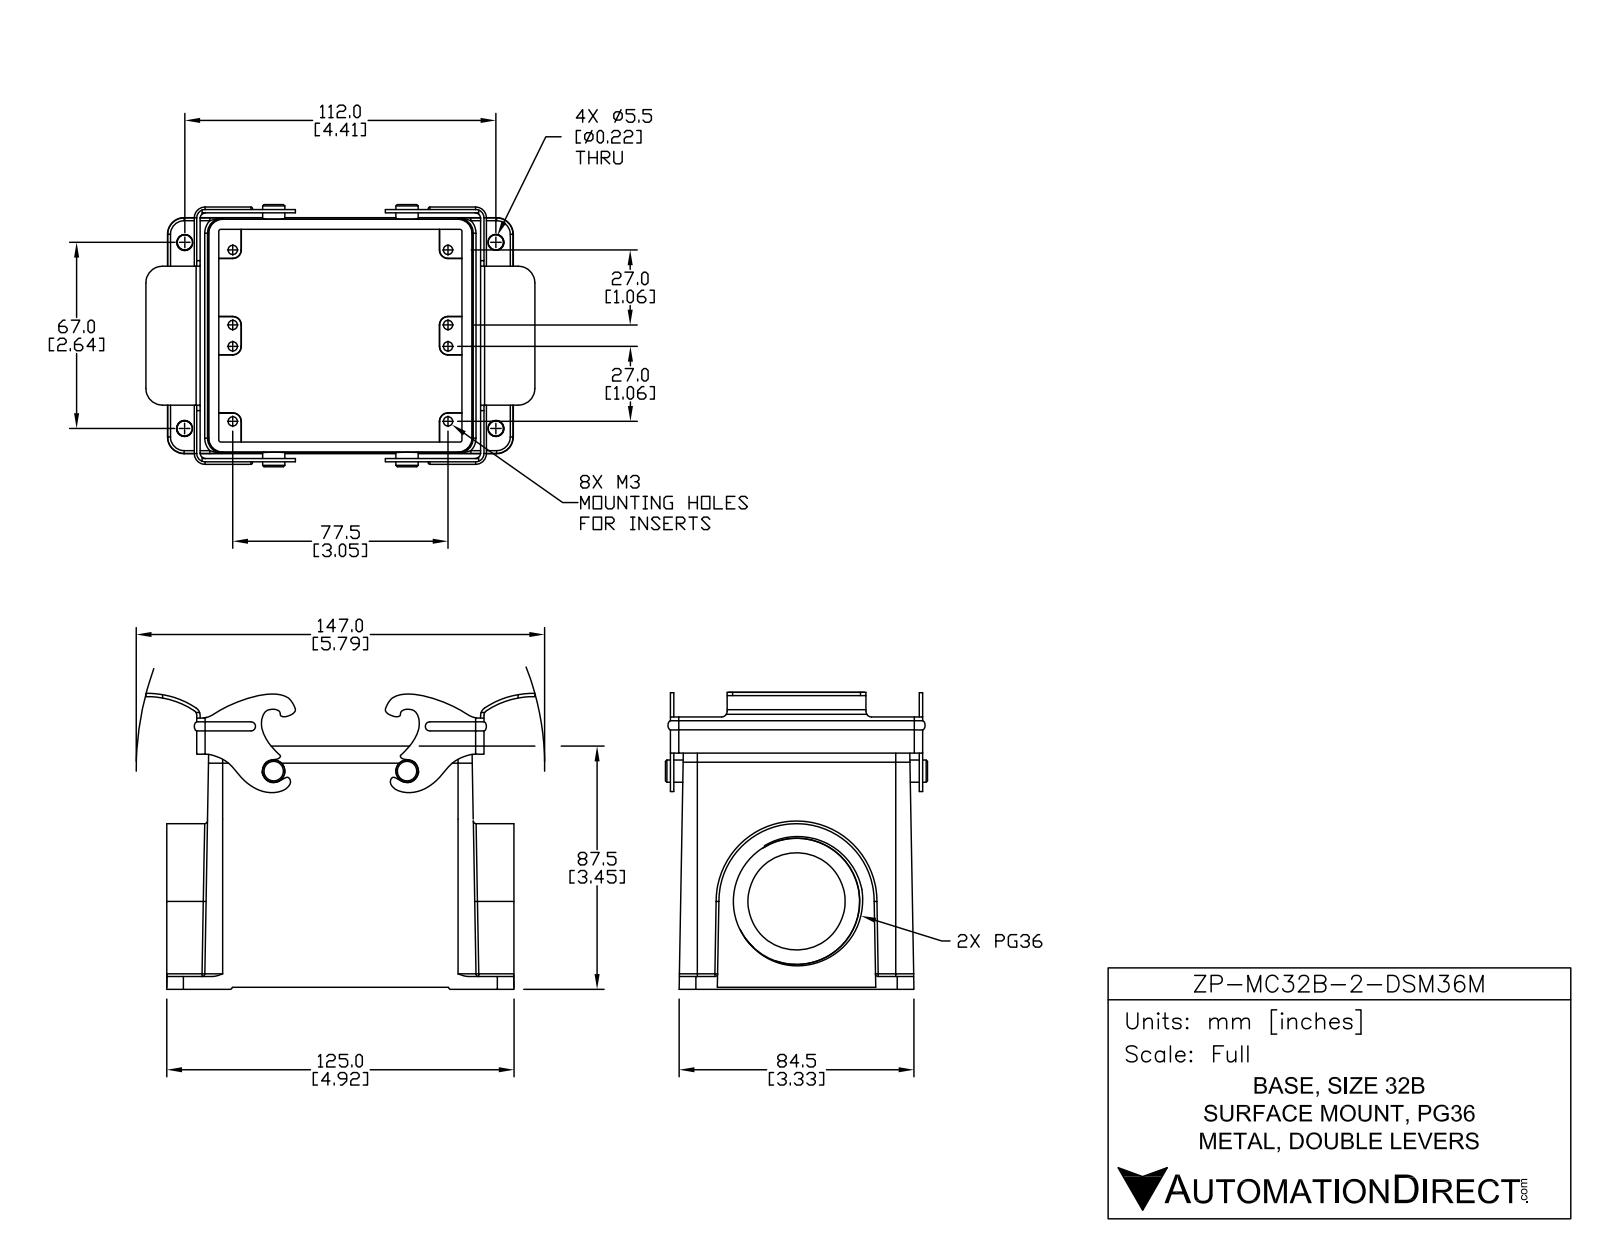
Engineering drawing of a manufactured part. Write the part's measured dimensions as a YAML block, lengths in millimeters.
part_name: "ZP-MC32B-2-DSM36M"
step_written_by: "SolidWorks 2014 (AUTOMOTIVE_DESIGN)"
units: millimeters
bodies: {solids: 1, faces: 357, planar: 127, cylindrical: 152, other: 78}
overall_size: [140.05, 107.5, 94.35]
volume: 261887
surface_area: 104508
round_holes:
  - {diameter: 3, count: 8}
  - {diameter: 35, count: 1}
  - {diameter: 45.5, count: 1}
round_bosses_or_shafts:
  - {diameter: 8.01, count: 2}
  - {diameter: 8, count: 2}
partial_cylinders:
  - {radius: 2, count: 12}
  - {radius: 1, count: 8}
  - {radius: 0.75, count: 4}
  - {radius: 3, count: 4}
  - {radius: 3.2, count: 2}
  - {radius: 30.4, count: 2}
  - {radius: 31.6, count: 2}
  - {radius: 27.95, count: 1}
face_to_face_distances: [72.95, 7.75, 1.2, 0.75, 8.5, 21, 104, 89.6, 12, 113]
hole_center_spacings: [27, 34.7, 77.5, 82.07, 84.91, 7.7, 61.7, 77.88]
